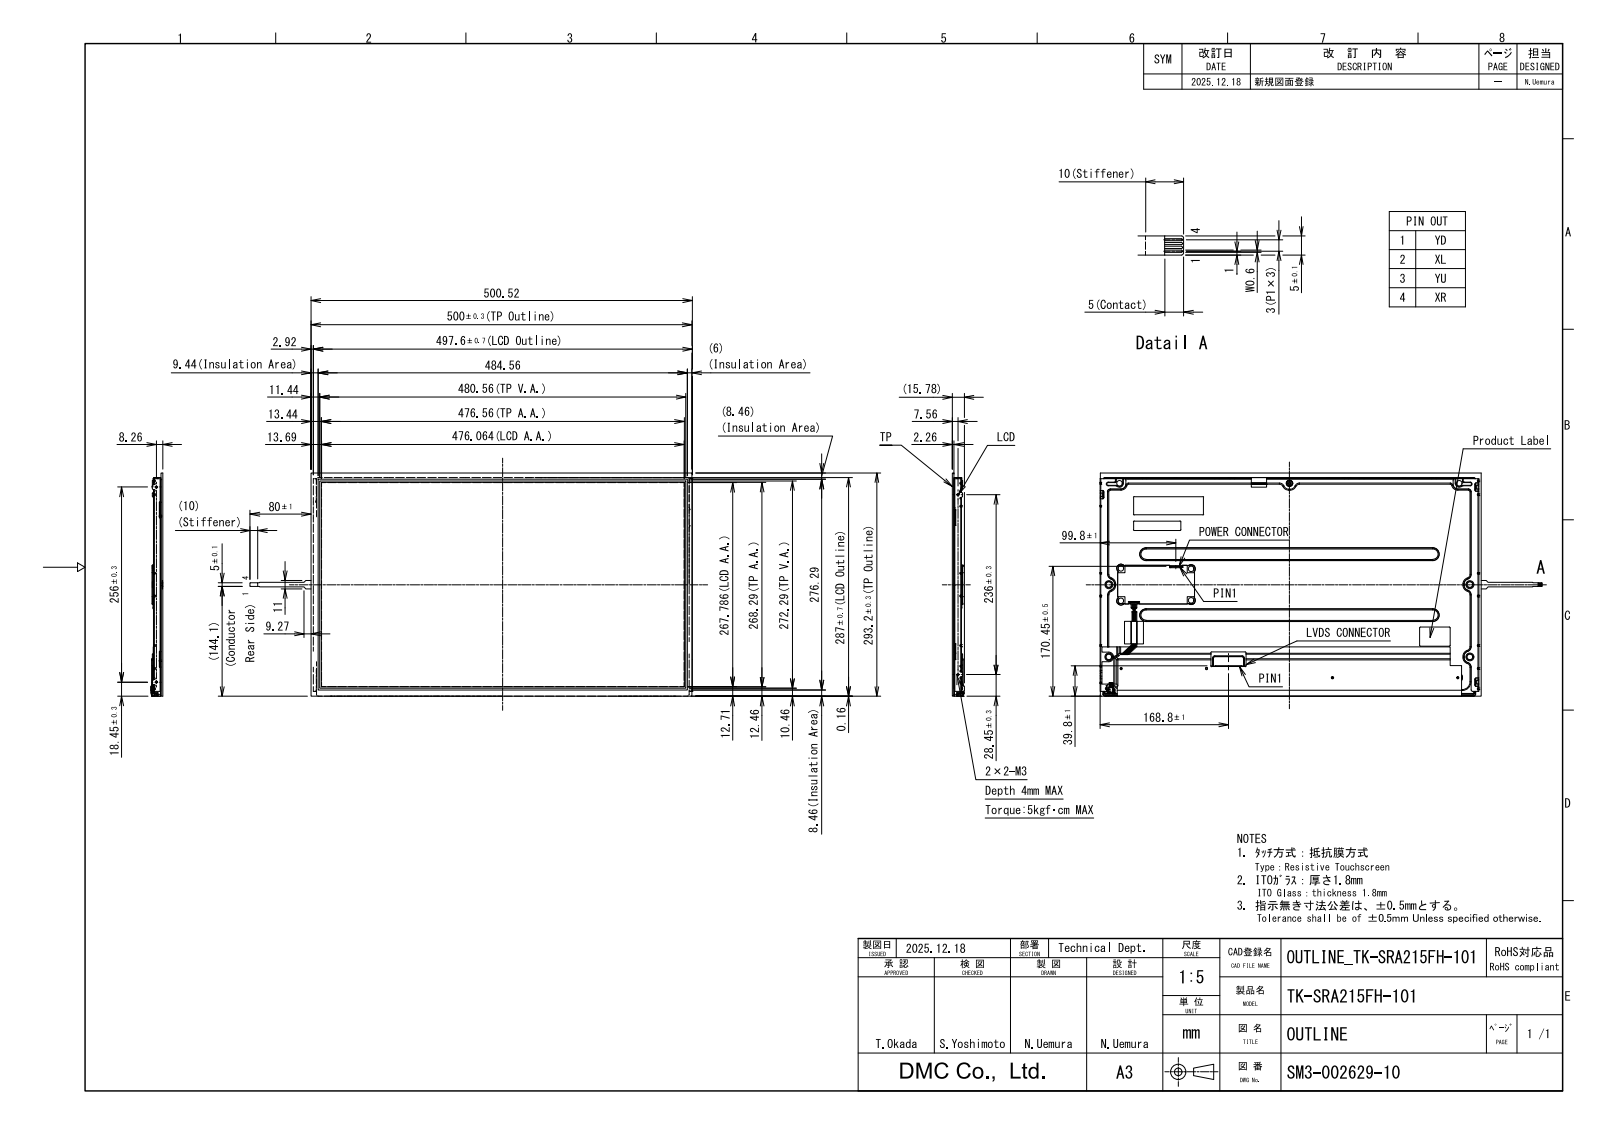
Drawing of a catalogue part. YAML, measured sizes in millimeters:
part_name: "HP-TK-SRA215FH-101"
step_written_by: "Autodesk Inventor 2024 (AUTOMOTIVE_DESIGN)"
units: millimeters
bodies: {solids: 1, faces: 11735, planar: 7349, cylindrical: 3472, other: 914}
overall_size: [580.52, 293.2, 15.78]
volume: 643000
surface_area: 800590
round_holes:
  - {diameter: 3, count: 10}
  - {diameter: 4, count: 4}
  - {diameter: 6.5, count: 4}
  - {diameter: 0.9, count: 2}
  - {diameter: 1.1, count: 2}
  - {diameter: 2.3, count: 2}
  - {diameter: 3.6, count: 2}
  - {diameter: 6, count: 2}
  - {diameter: 8, count: 2}
  - {diameter: 2, count: 1}
round_bosses_or_shafts:
  - {diameter: 0.87, count: 47}
  - {diameter: 4.6, count: 7}
  - {diameter: 7.5, count: 6}
  - {diameter: 3, count: 6}
  - {diameter: 2.5, count: 6}
  - {diameter: 7, count: 4}
  - {diameter: 4.5, count: 4}
  - {diameter: 4, count: 4}
partial_cylinders:
  - {radius: 0.1, count: 641}
  - {radius: 0.2, count: 387}
  - {radius: 1, count: 232}
  - {radius: 0.5, count: 205}
  - {radius: 0.3, count: 162}
  - {radius: 0.15, count: 127}
  - {radius: 0.7, count: 110}
  - {radius: 0.9, count: 49}
face_to_face_distances: [0.8, 3.31, 9.86, 9.06, 6.55, 5.75, 0.5, 1.3, 1.8, 2.1]
hole_center_spacings: [5.9, 10.02, 92, 101.13, 106.12, 112.02, 165.81, 223]
